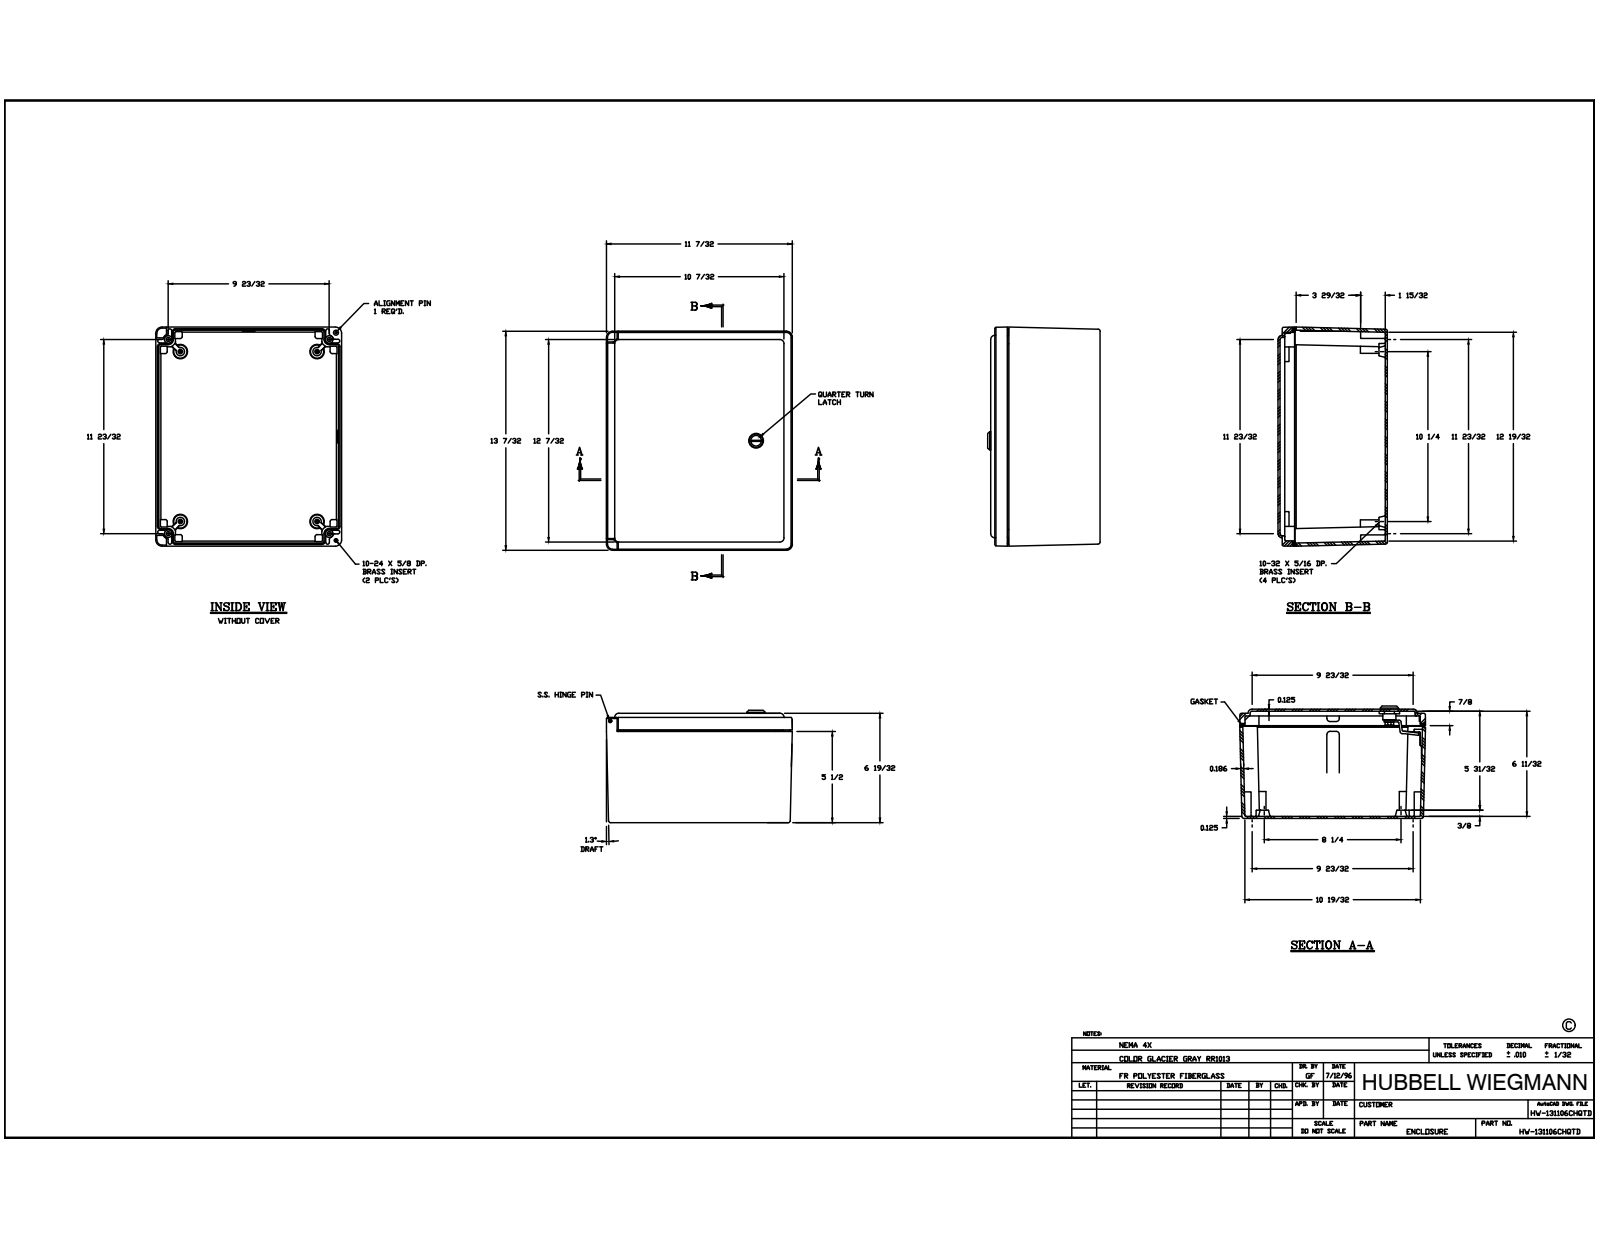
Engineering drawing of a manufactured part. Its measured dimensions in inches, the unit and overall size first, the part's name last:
Units: inches
Overall size (bounding box): 13.219 × 11.223 × 6.781
Round holes (diameter × count): ⌀0.281 ×6, ⌀0.156 ×4, ⌀0.313 ×4, ⌀0.531 ×4, ⌀0.096 ×2, ⌀0.104 ×2, ⌀0.13 ×2, ⌀0.14 ×2, ⌀0.145 ×2, ⌀0.156 ×2, ⌀0.179 ×2, ⌀0.187 ×2
Round bosses / shafts (diameter × count): ⌀0.375 ×2, ⌀0.371 ×2, ⌀0.234 ×2, ⌀0.095 ×2, ⌀1.094 ×1, ⌀0.63 ×1, ⌀0.4 ×1, ⌀0.367 ×1
Partial cylindrical surfaces — rounded edges, fillets, slot ends (radius × count): R0.031 ×60, R0.125 ×38, R0.063 ×29, R0.313 ×11, R0.059 ×8, R0.188 ×8, R0.25 ×8, R0.375 ×8
Main face-to-face distances: 0.125, 6.469, 0.186, 6.594, 6.344, 0.125, 0.25, 6.344, 6.219, 0.75
Hole centre spacings: 1.039, 6.534, 9.014, 11.008, 11.447, 12.131, 12.531, 14.19
Volume: 110.1 in³ · Surface area: 1 310 in²
Bodies: 28 solids, 1095 faces (446 planar, 333 cylindrical, 316 other)
Part name (STEP PRODUCT): WP1311HLBOX; 0.3125-18 X 0.563 DP BRASS INSERT; 10-32 X0.3125 DP BRASS INSERT; 10-24 X 0.625 DP BRASS INSERT (+8 more)
STEP written by: Autodesk Inventor 2014 (AUTOMOTIVE_DESIGN)
